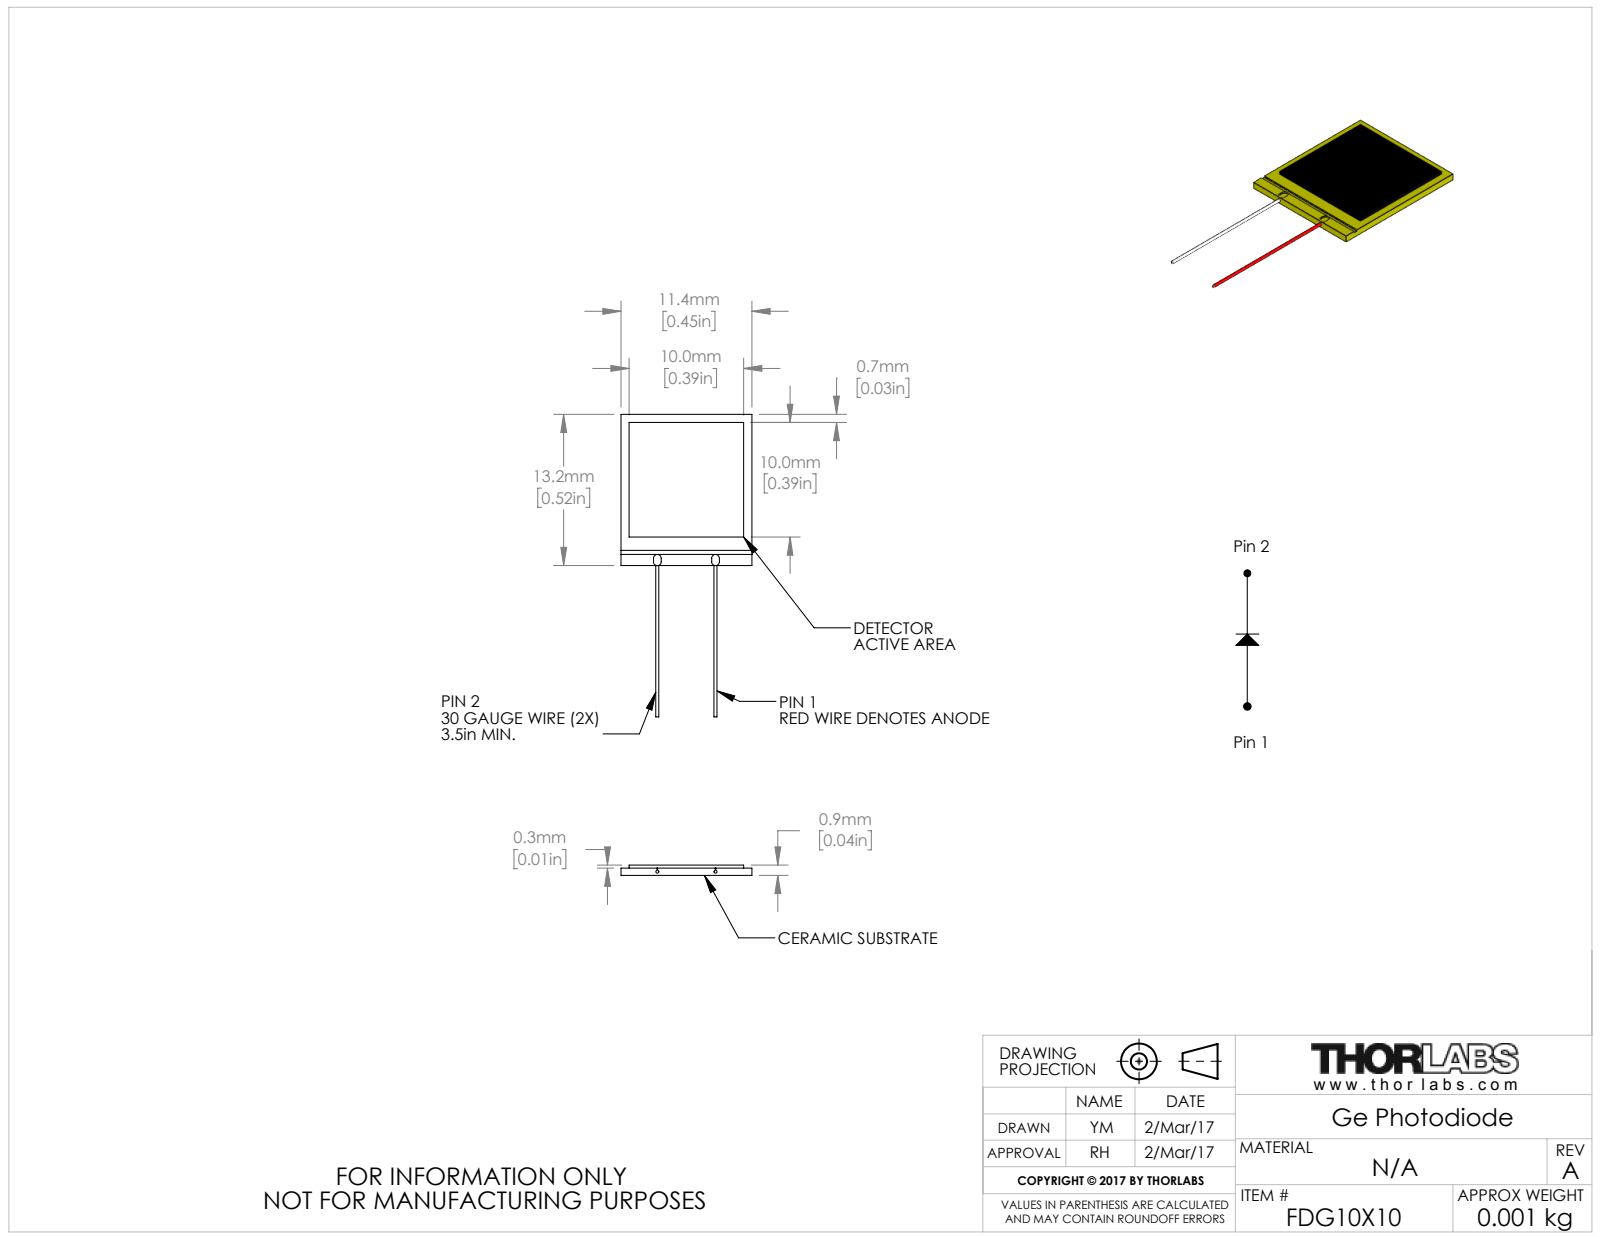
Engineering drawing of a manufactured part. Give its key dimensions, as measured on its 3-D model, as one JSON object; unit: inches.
{"part_name": "TTN126580-E0W", "step_written_by": "SolidWorks 2016 (AUTOMOTIVE_DESIGN)", "units": "inches", "bodies": {"solids": 3, "faces": 41, "planar": 27, "cylindrical": 14, "other": 0}, "overall_size": [1.04, 0.45, 0.035], "volume_in3": 0.007, "surface_area_in2": 0.571, "round_bosses_or_shafts": [[0.01, 2]], "partial_cylinders_radius": [[0.013, 4]], "face_to_face_distances": [0.035, 0.025, 0.45, 0.52, 0.02, 0.015, 0.028, 0.422, 0.394, 0.098]}
